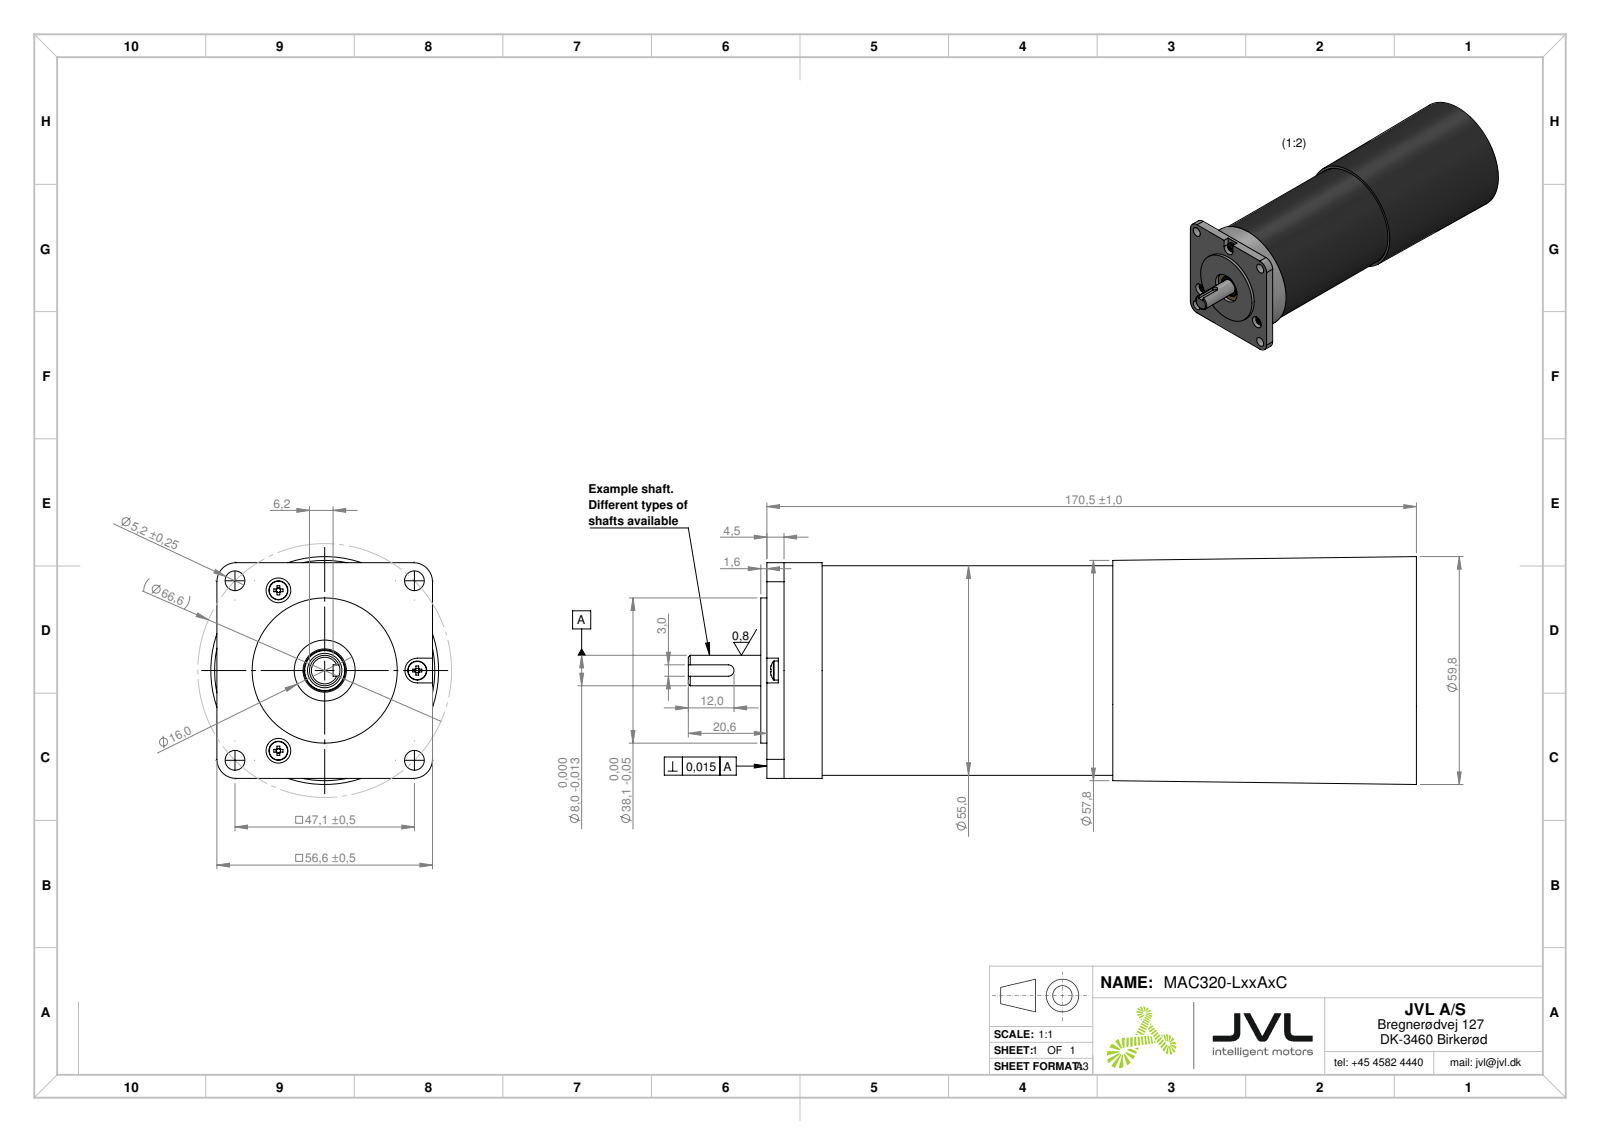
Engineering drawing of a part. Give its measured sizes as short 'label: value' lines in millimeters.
name: MAC320-XXXXXX-X (ShØ8-key, IP42-long); MAC050-320-HOUSE-mockup (MM0315)_DEFAULT; MAC050-320-BHOUSE (mockup)_no STO; MAC050-320-MTRBASE-mockup_MAC141-320 (+5 more)
written by: SolidWorks 2023 (AUTOMOTIVE_DESIGN)
unit: mm
bodies: 20 solids, 681 faces (232 planar, 170 cylindrical, 279 other)
size: 197 × 59.5 × 59.5
volume: 107 927 mm³; area: 81 717 mm²
holes: 6× ⌀2.05, 4× ⌀5.2, 3× ⌀2.5, 3× ⌀6.2, 1× ⌀2, 1× ⌀8, 1× ⌀9, 1× ⌀10, 1× ⌀10.76, 1× ⌀11.37, 1× ⌀17.18, 1× ⌀18
bosses: 3× ⌀2.5, 2× ⌀2.25, 1× ⌀56.6, 1× ⌀55, 1× ⌀38.1, 1× ⌀28, 1× ⌀22, 1× ⌀17.47
rounds: 36× R0.24, 4× R1, 4× R5, 2× R2.5, 2× R4, 1× R1.5, 1× R26.68
face distances: 115.1, 119.7, 4.6, 6, 109.1, 113.7, 121.3, 115.3, 6.2, 1.6
hole spacings: 33.3, 47.1, 0.66, 24.3, 24.8, 42.73, 10.74, 11.67
